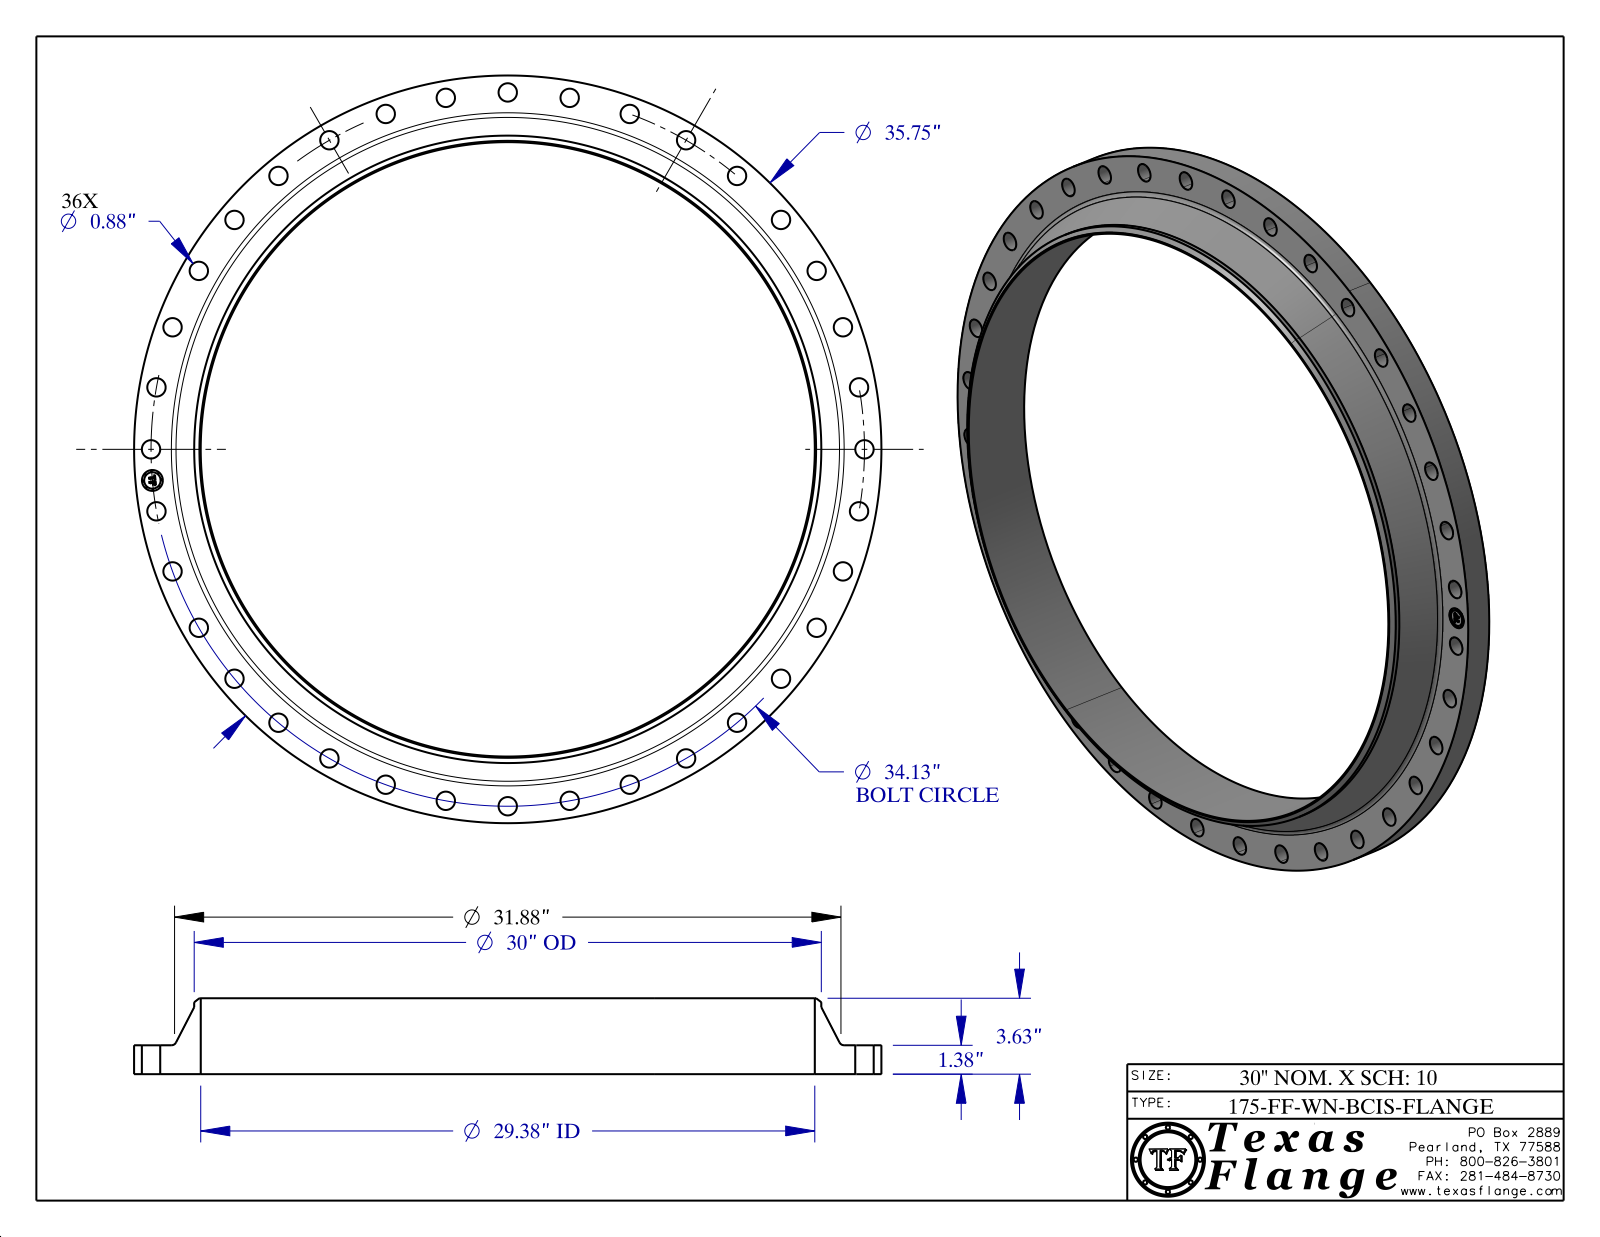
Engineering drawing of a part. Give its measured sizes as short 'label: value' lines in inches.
name: 175-FF-WN, BCIS
written by: CATIA V5 STEP AP214 (AUTOMOTIVE_DESIGN)
unit: in
bodies: 1 solid, 472 faces (368 planar, 98 cylindrical, 6 other)
size: 35.75 × 35.75 × 3.63
volume: 565.7 in³; area: 1 369 in²
holes: 36× ⌀0.88, 1× ⌀1, 1× ⌀29.376
bosses: 8× ⌀0.061, 1× ⌀35.75, 1× ⌀30, 1× ⌀0.788
face distances: 1.38, 3.63, 2.25, 1.365, 0.015, 2.265, 0.298, 0.293, 0.054, 0.193
hole spacings: 17.065, 34, 2.975, 29.557, 8.833, 5.927, 26.145, 30.932
